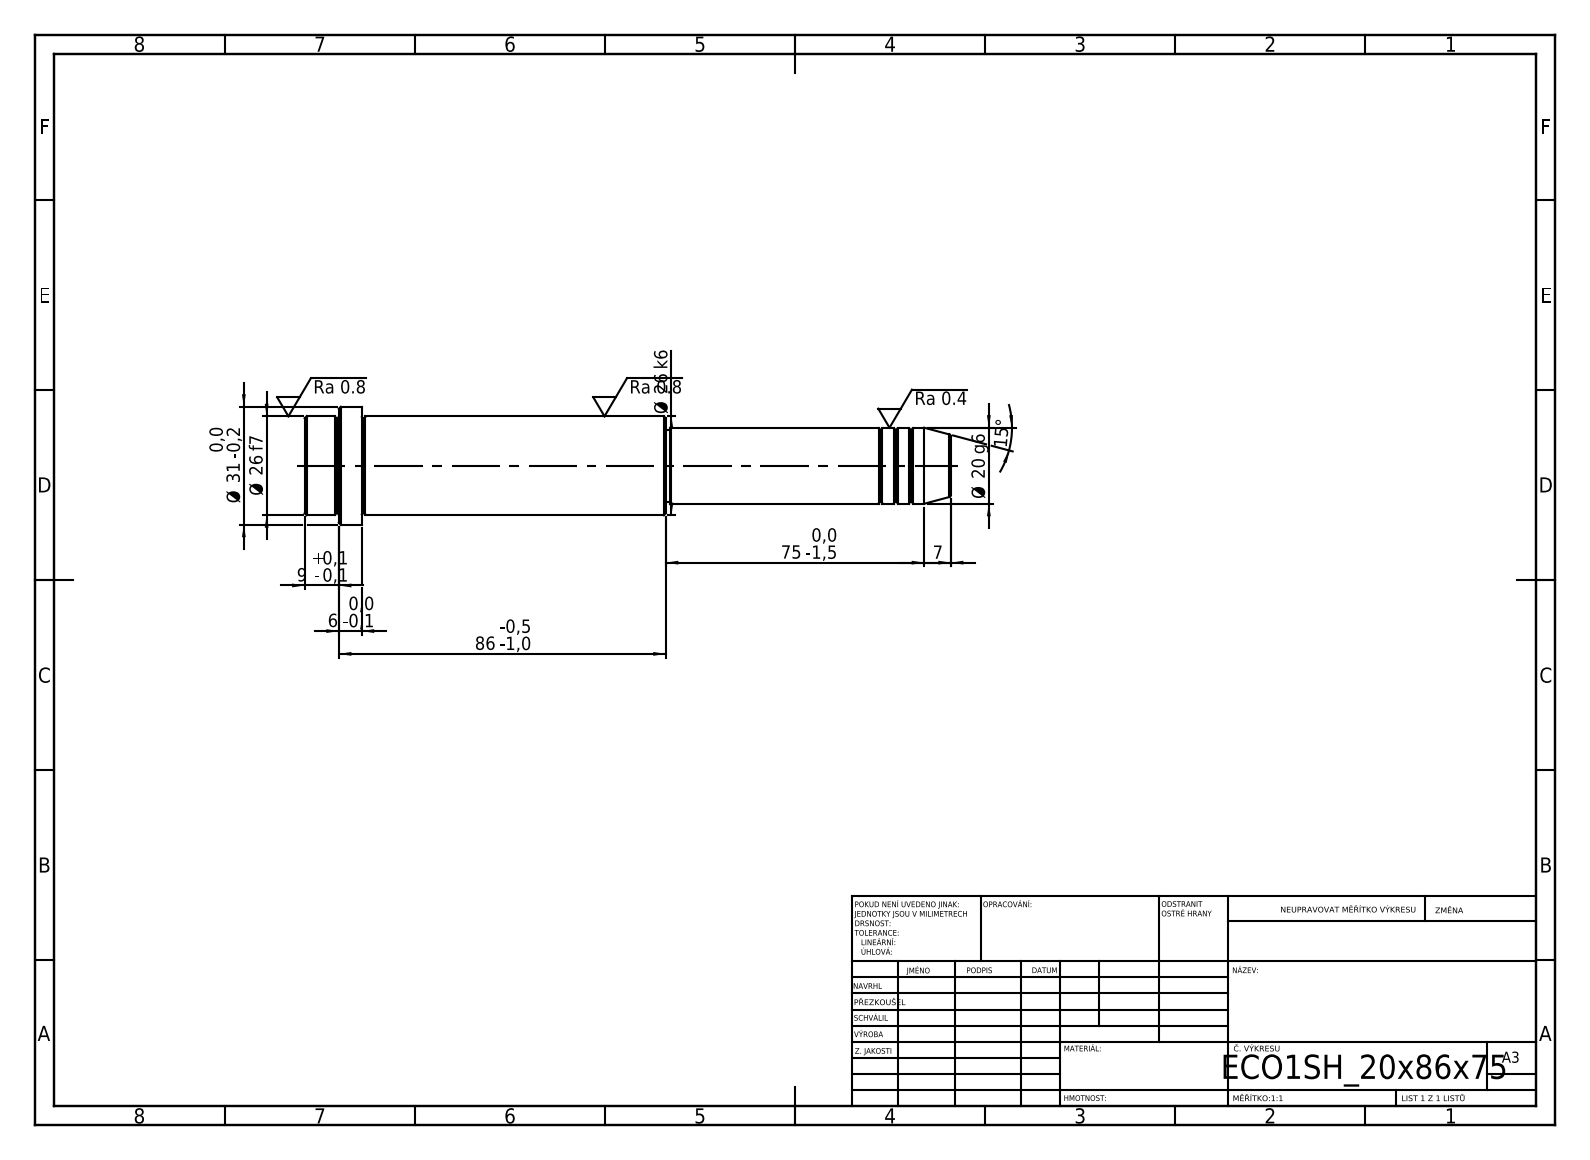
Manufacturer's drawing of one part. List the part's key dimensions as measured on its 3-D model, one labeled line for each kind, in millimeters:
STEP written by: SolidWorks 2019 (CONFIG_CONTROL_DESIGN)
Units: millimetres
Bodies: 1 solid, 52 faces (6 planar, 16 cylindrical, 30 other)
Overall size (bounding box): 170 × 31 × 31
Volume: 74 757 mm³ · Surface area: 14 102 mm²
Round bosses / shafts (diameter × count): ⌀31 ×1, ⌀26 ×1, ⌀20 ×1, ⌀19 ×1
Main face-to-face distances: 15, 80, 95, 75, 155, 170, 161, 86, 6, 9
